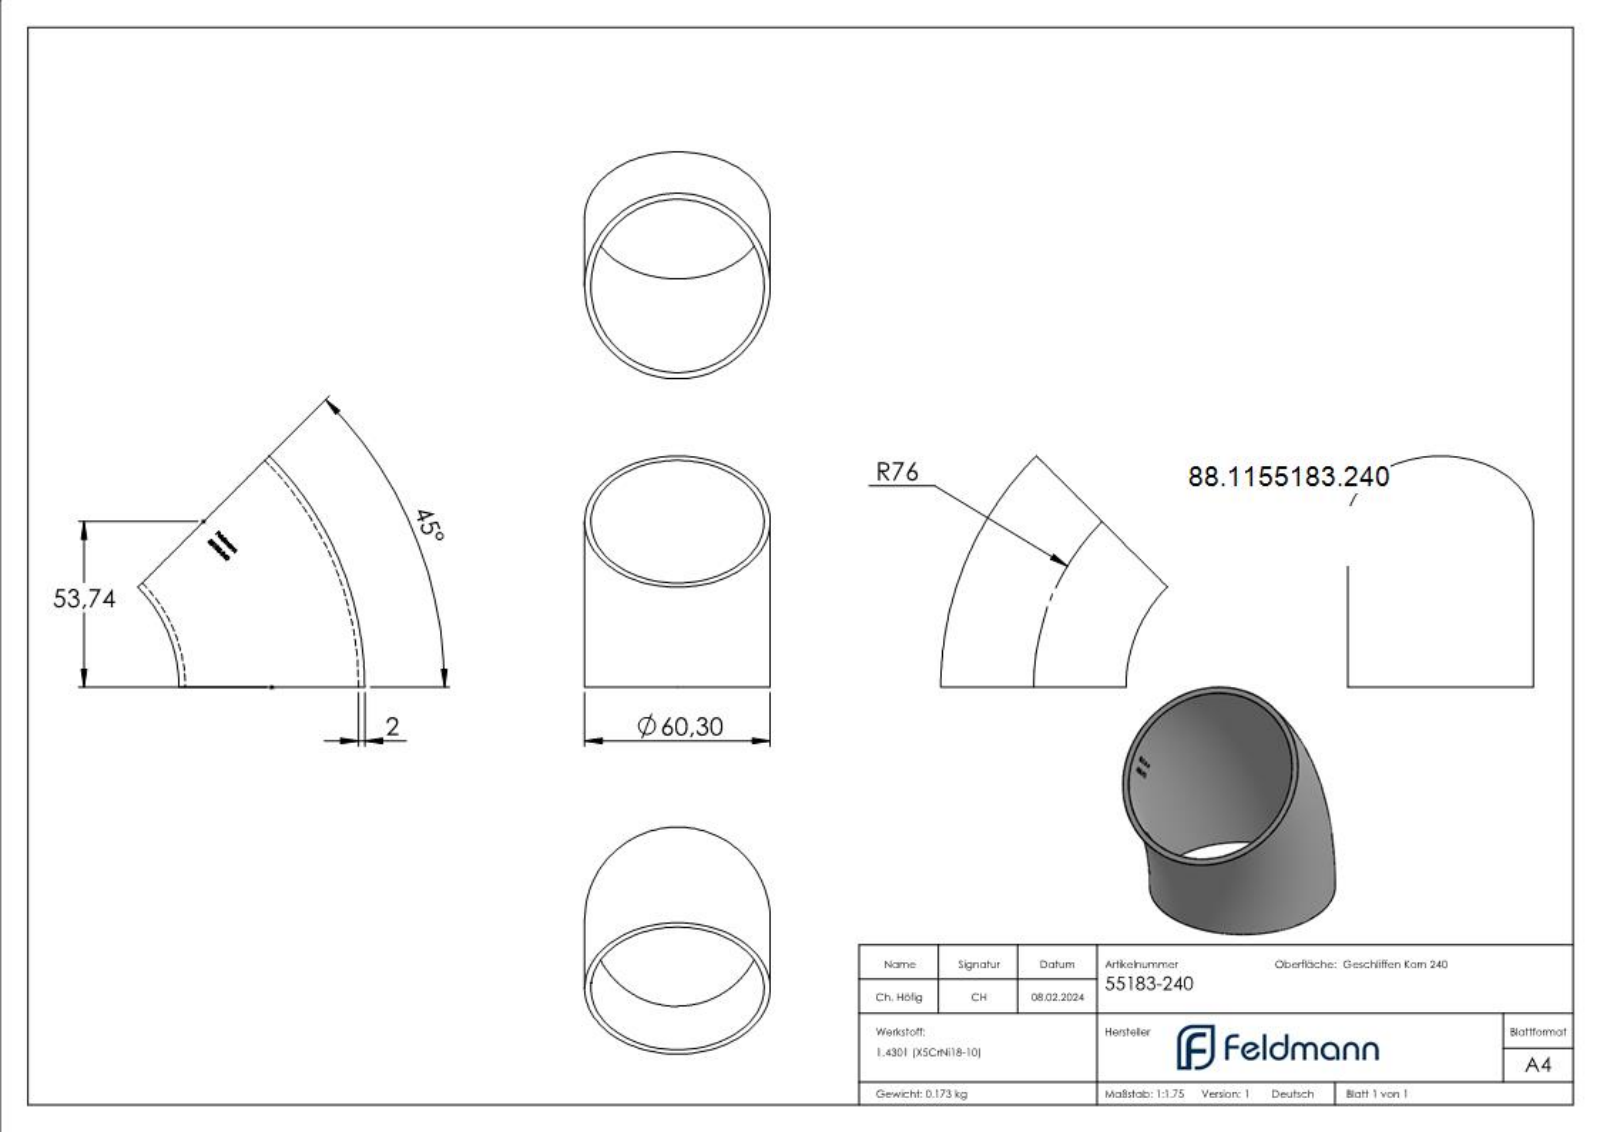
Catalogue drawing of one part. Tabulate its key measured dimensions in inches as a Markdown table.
| quantity | value |
| --- | --- |
| part name | 55183-240 |
| STEP written by | SolidWorks 2018 (CONFIG_CONTROL_DESIGN) |
| units | inches |
| bodies | 1 solid, 236 faces (100 planar, 0 cylindrical, 136 other) |
| overall size | 2.955 × 2.903 × 2.374 |
| volume | 1.334 in³ |
| surface area | 35.04 in² |
| main face-to-face distances | 0.117, 0.193, 0.048, 0.133, 0.039, 0.095, 0.021, 0.159, 0.144, 0.141 |
